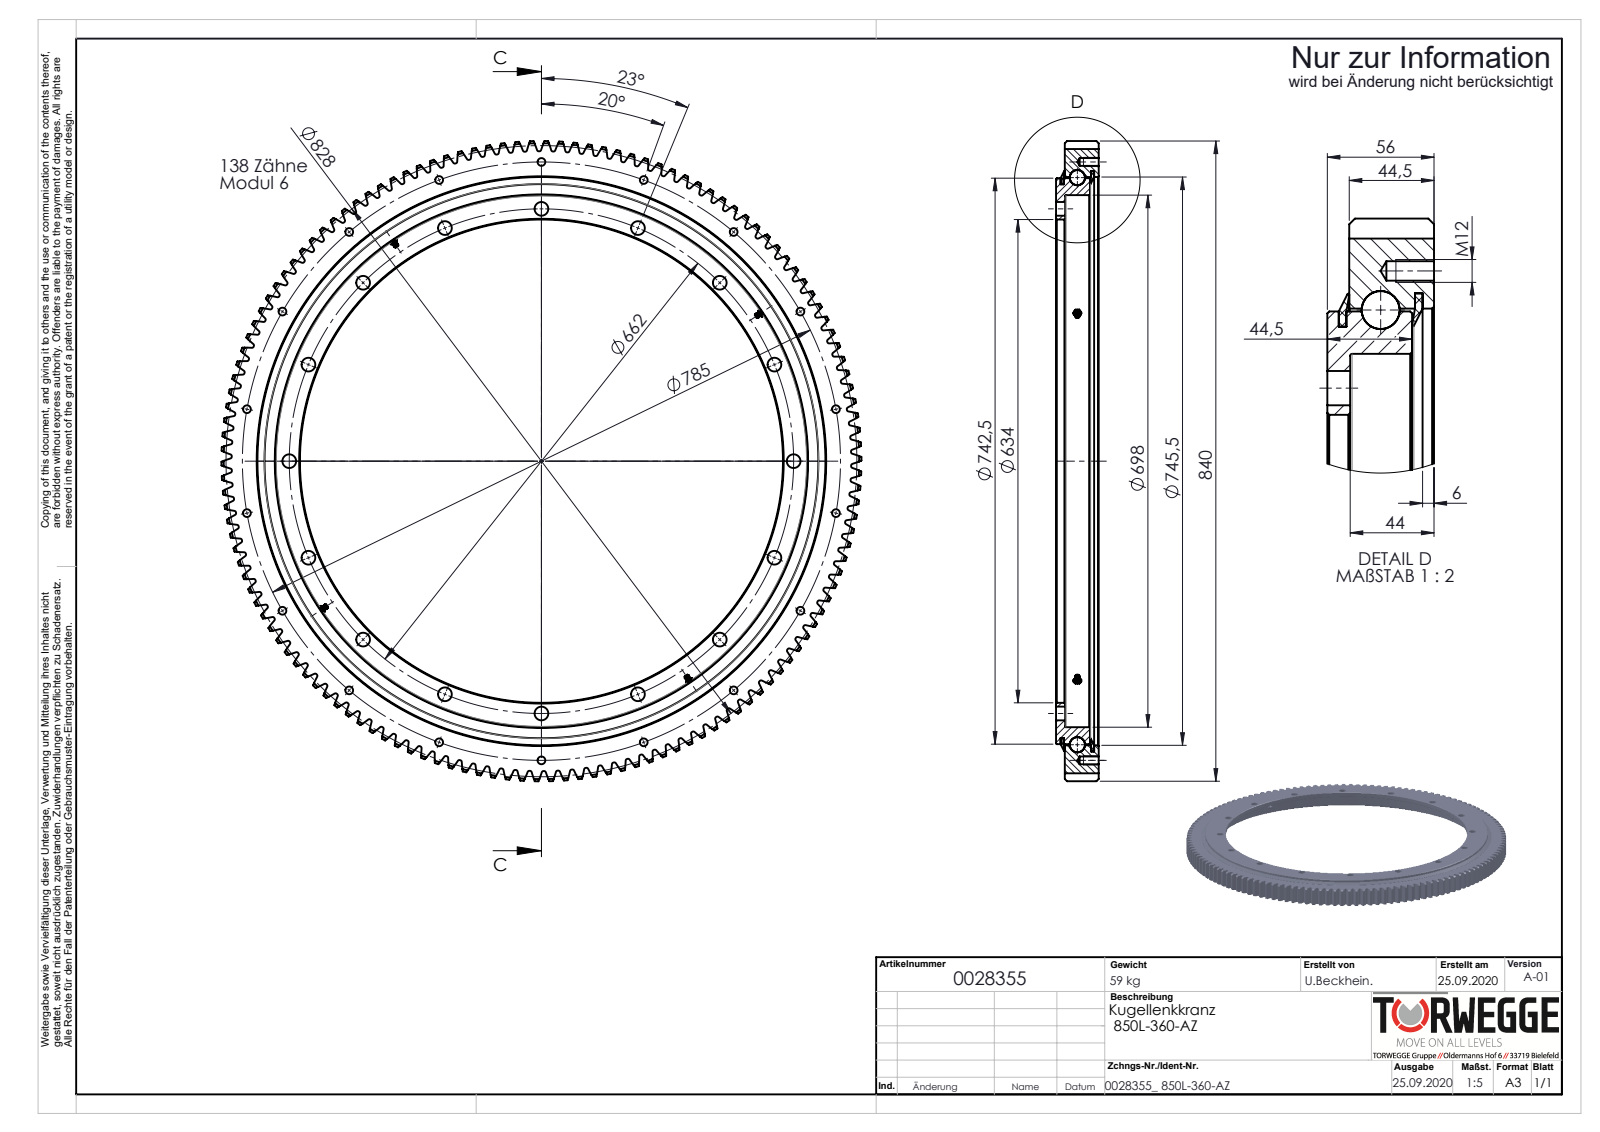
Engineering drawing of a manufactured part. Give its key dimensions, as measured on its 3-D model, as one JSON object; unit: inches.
{"part_name": "0028355", "step_written_by": "SolidWorks 2018 (AUTOMOTIVE_DESIGN)", "units": "inches", "bodies": {"solids": 12, "faces": 967, "planar": 62, "cylindrical": 286, "other": 619}, "overall_size": [33.071, 33.069, 2.205], "volume_in3": 370, "surface_area_in2": 1998, "round_holes": [[0.402, 18], [0.709, 16], [0.059, 4], [0.079, 4], [0.177, 4], [0.276, 2], [0.197, 1], [0.866, 1], [24.961, 1], [27.48, 1], [28.602, 1], [29.35, 1]], "round_bosses_or_shafts": [[0.315, 4], [0.157, 4], [29.981, 1], [29.232, 1], [0.862, 1]], "partial_cylinders_radius": [[16.535, 1]], "face_to_face_distances": [0.453, 1.752, 0.236, 1.732, 2.205, 0.217, 0.394, 1.811, 0.059, 1.358], "hole_center_spacings": [15.453, 5.085, 13.031, 18.429, 21.67, 9.974, 5.367, 10.57]}
